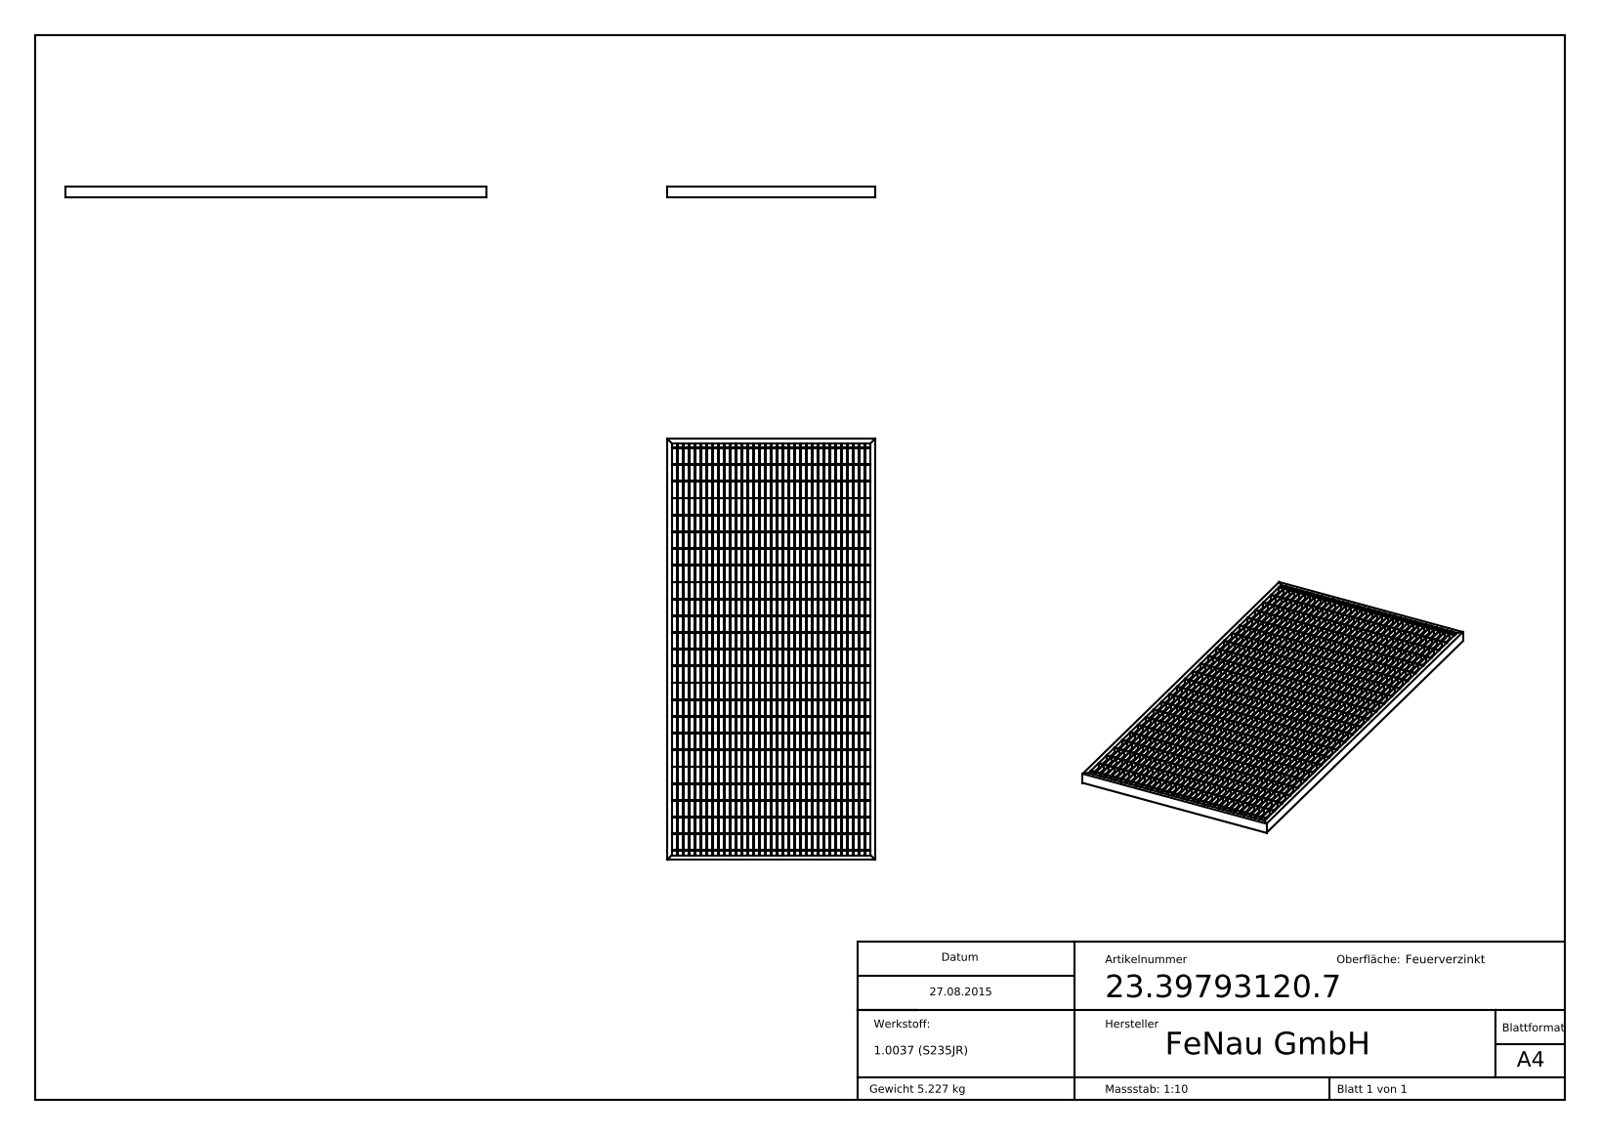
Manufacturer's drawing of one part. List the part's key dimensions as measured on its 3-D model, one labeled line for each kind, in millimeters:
Part name (STEP PRODUCT): 23-39793120-7
STEP written by: SolidWorks 2015 (CONFIG_CONTROL_DESIGN)
Units: millimetres
Bodies: 1 solid, 3034 faces (3034 planar, 0 cylindrical, 0 other)
Overall size (bounding box): 790 × 390 × 20
Volume: 670 182 mm³ · Surface area: 1 091 000 mm²
Main face-to-face distances: 94.5, 31.5, 63, 11, 22, 126, 33, 157.5, 44, 189
